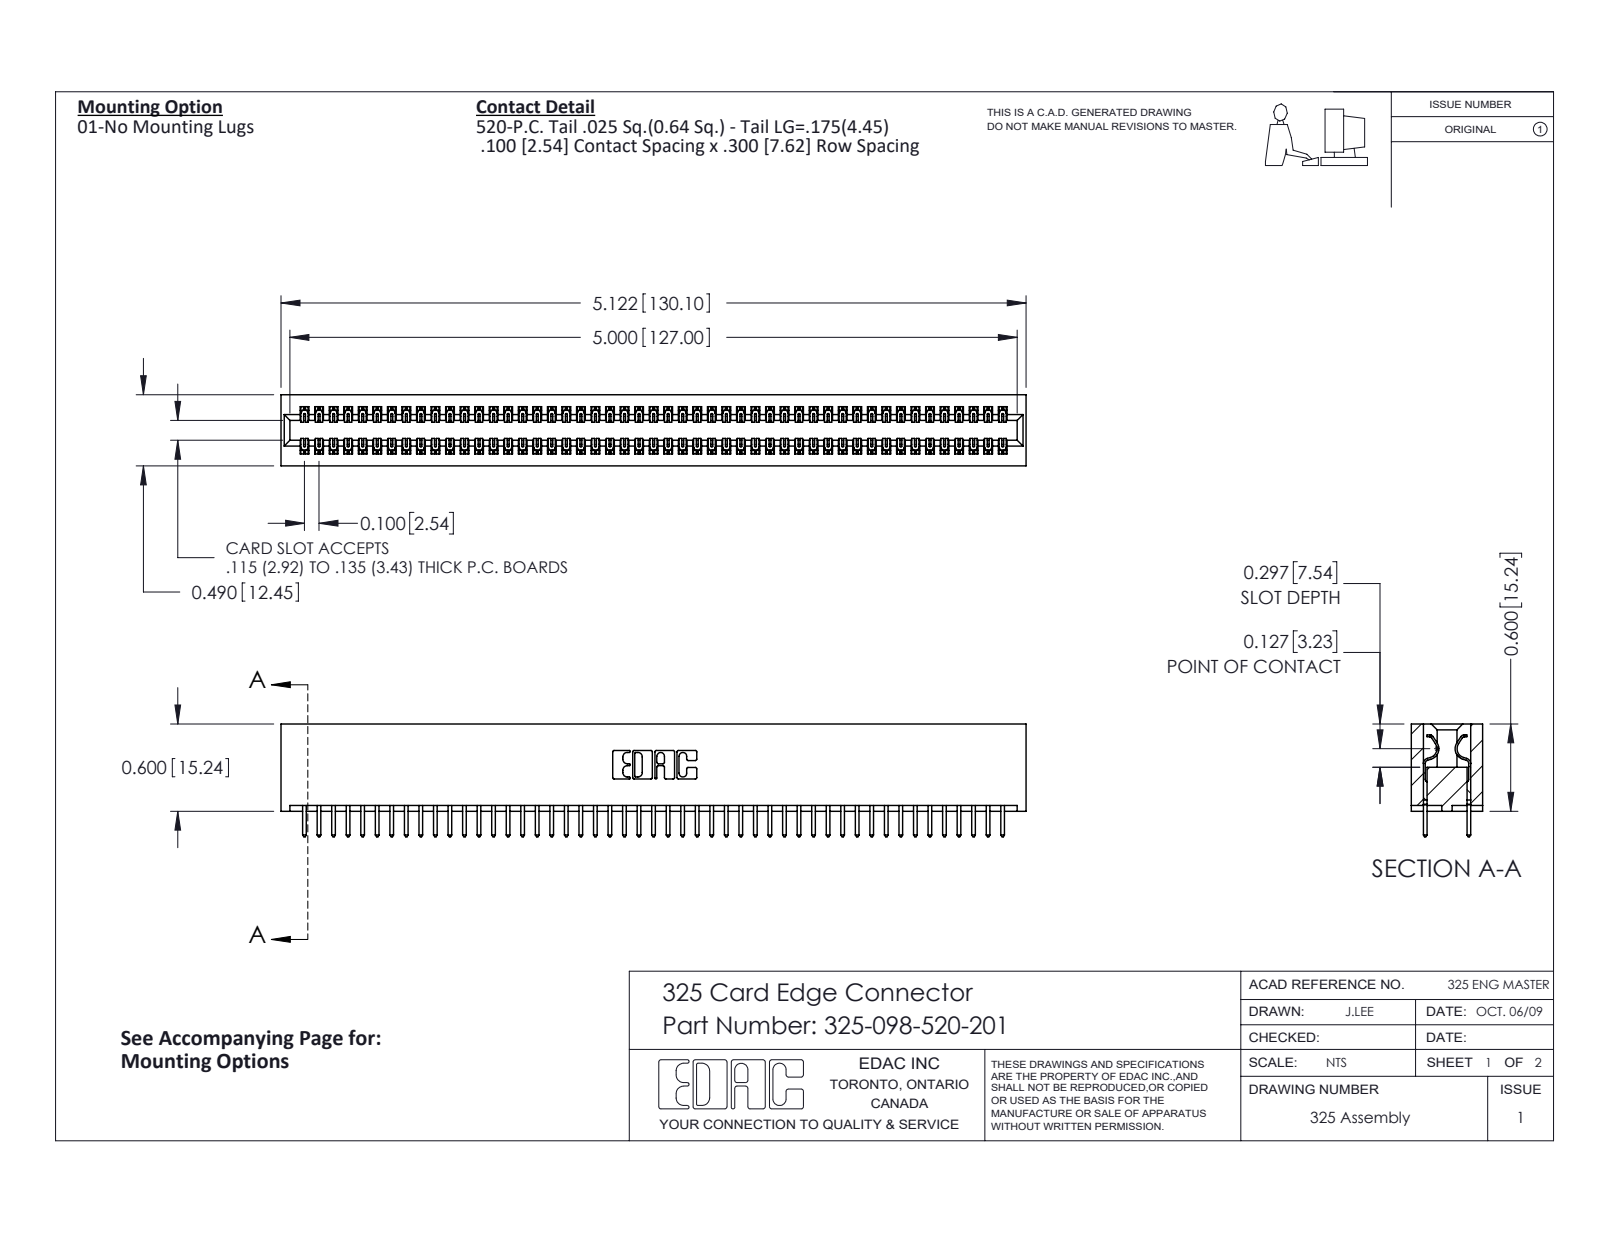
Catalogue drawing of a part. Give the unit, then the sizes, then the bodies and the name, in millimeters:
Units: millimetres
Overall size (bounding box): 130.1 × 19.7 × 12.4
Partial cylindrical surfaces — rounded edges, fillets, slot ends (radius × count): R0.2 ×147, R0.3 ×98, R0.3 ×22, R0.2 ×6, R0.8 ×6, R0.7 ×3, R0.4 ×2, R0.6 ×2
Main face-to-face distances: 2.1, 10.3, 7.6, 12.4, 2.7, 9.7, 0.6, 8.3, 7, 14.2
Volume: 17 450 mm³ · Surface area: 21 750 mm²
Bodies: 99 solids, 5202 faces (3594 planar, 1608 cylindrical, 0 other)
Part name (STEP PRODUCT): 325-292-001_325-293-120; 325 Part_Lugless; 325-098-520-201
STEP written by: SolidWorks 2016 (CONFIG_CONTROL_DESIGN)
